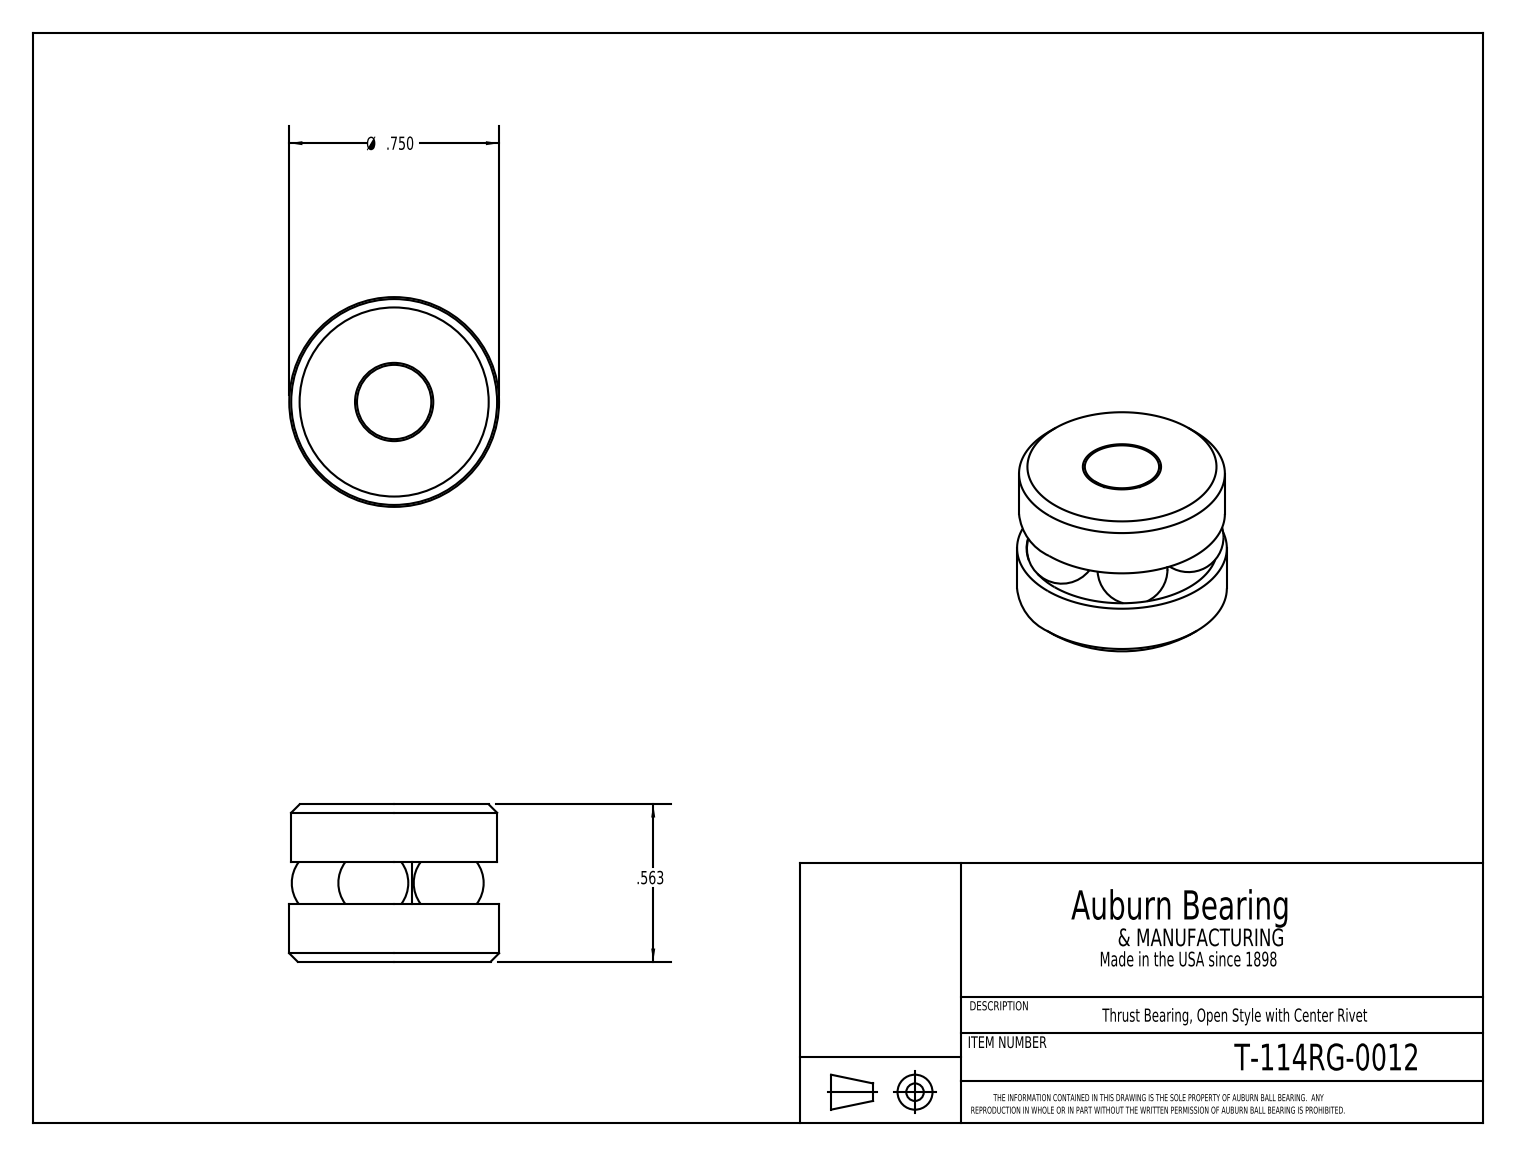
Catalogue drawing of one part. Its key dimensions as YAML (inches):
part_name: "T-114RG_T-114RG-0012"
step_written_by: "SolidWorks 2016 (CONFIG_CONTROL_DESIGN)"
units: inches
bodies: {solids: 8, faces: 26, planar: 8, cylindrical: 5, other: 13}
overall_size: [0.75, 0.75, 0.563]
volume: 0.197
surface_area: 4.185
round_holes:
  - {diameter: 0.135, count: 1}
  - {diameter: 0.135, count: 1}
round_bosses_or_shafts:
  - {diameter: 0.75, count: 1}
  - {diameter: 0.736, count: 1}
  - {diameter: 0.125, count: 1}
face_to_face_distances: [0.563, 0.206, 0.356, 0.15]
